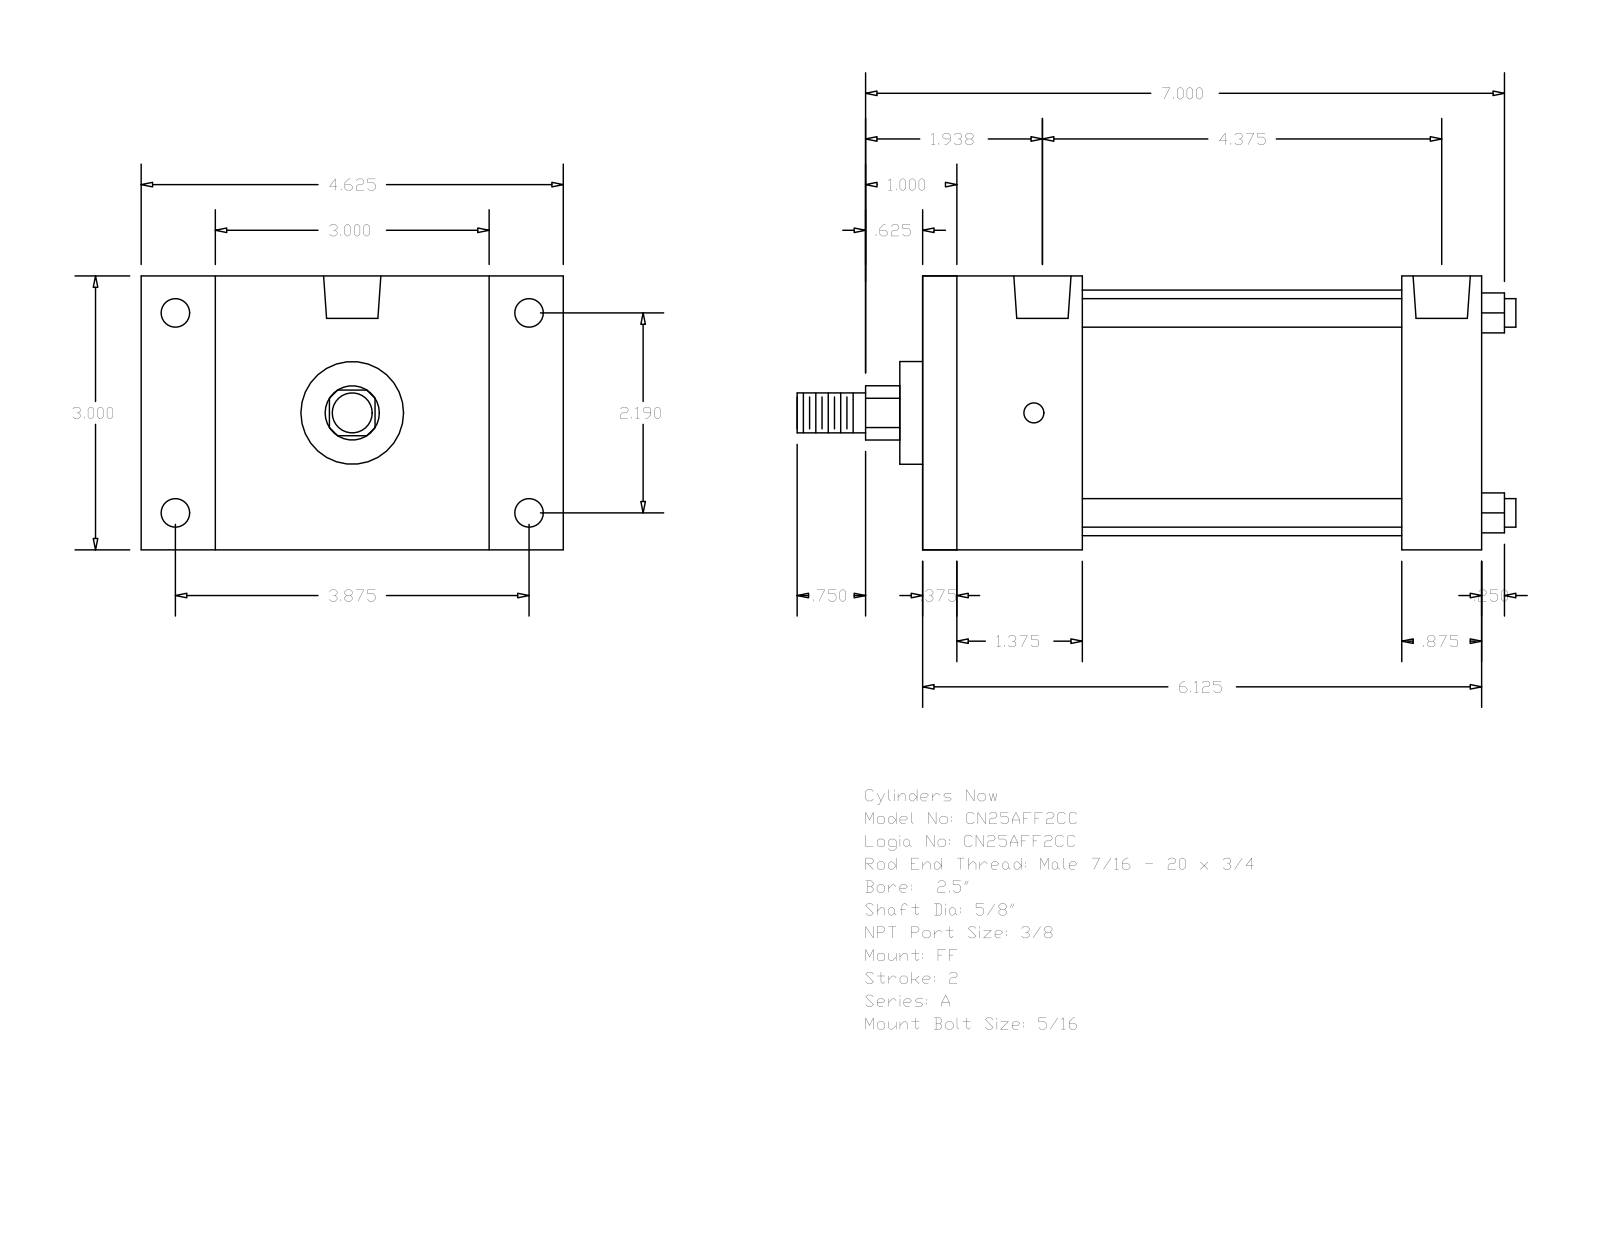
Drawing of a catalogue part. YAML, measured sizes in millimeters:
part_name: "A_FF__0250_0.625"
step_written_by: "GSSL Pune (CONFIG_CONTROL_DESIGN)"
units: millimeters
bodies: {solids: 0, faces: 92, planar: 64, cylindrical: 28, other: 0}
overall_size: [200.03, 117.47, 76.2]
round_holes:
  - {diameter: 5.56, count: 4}
  - {diameter: 7.94, count: 4}
  - {diameter: 15.93, count: 2}
round_bosses_or_shafts:
  - {diameter: 7.94, count: 4}
  - {diameter: 68.33, count: 1}
  - {diameter: 28.57, count: 1}
  - {diameter: 15.88, count: 1}
  - {diameter: 11.11, count: 1}
partial_cylinders:
  - {radius: 7.54, count: 1}
face_to_face_distances: [76.2, 155.57, 9.52, 146.05, 44.45, 34.93, 133.34, 123.82, 88.89, 111.12]
hole_center_spacings: [2.38, 55.62, 98.42, 113.05, 113.51, 115.89, 111.13]
